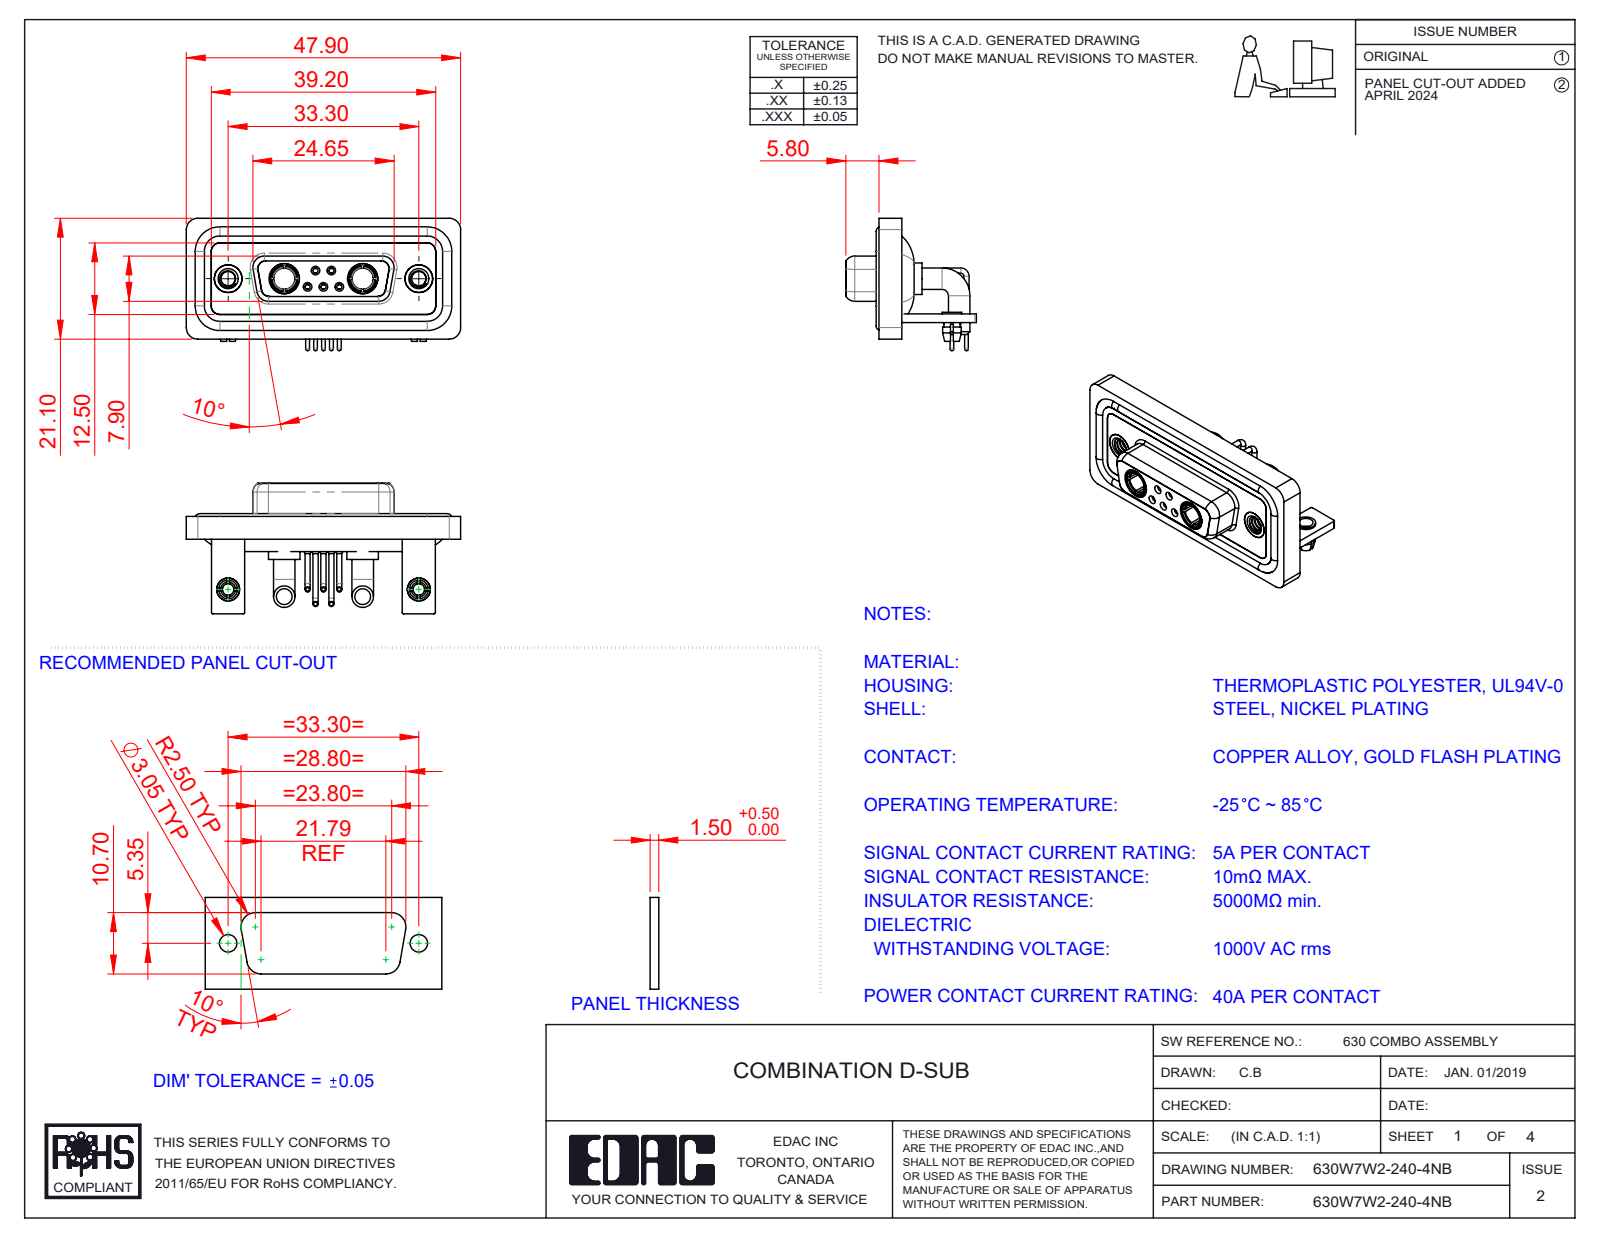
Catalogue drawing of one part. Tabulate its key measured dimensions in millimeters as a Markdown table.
| quantity | value |
| --- | --- |
| part name | 630Combo Threaded Rivet_A; 630Combo Shell Rear_15 Contacts; 630Combo Housing_7W2; 630Combo Contact Row 2_50 Contacts (+7 more) |
| STEP written by | SolidWorks 2023 (CONFIG_CONTROL_DESIGN) |
| units | millimeters |
| bodies | 20 solids, 941 faces (306 planar, 407 cylindrical, 228 other) |
| overall size | 47.9 × 23.12 × 22.8 |
| volume | 6 737 mm³ |
| surface area | 11 242 mm² |
| round holes (diameter × count) | 2 × 7, 0.9 × 5, 1.1 × 5, 1.5 × 5, 2.5 × 4, 4.85 × 4, 1.6 × 3, 1.7 × 2, 3.2 × 2, 3.7 × 2, 4 × 2, 4.05 × 2 |
| round bosses / shafts (diameter × count) | 1.6 × 6, 0.9 × 5, 0.65 × 5, 3.75 × 4, 5.5 × 2, 5.2 × 2, 4.96 × 2, 4.95 × 2 |
| partial cylindrical surfaces (radius × count) | 2 × 21, 1.5 × 18, 0.25 × 16, 1.35 × 12, 1.6 × 8, 0.5 × 5, 0.6 × 4, 0.65 × 4 |
| main face-to-face distances | 0.4, 2.9, 1.5, 1.8, 3.7, 1.1, 4.1, 1.6, 2.5, 1.4 |
| hole center spacings | 3.16, 2.77, 9.8, 23.5, 33.3, 4.31, 4.33, 5.03 |
